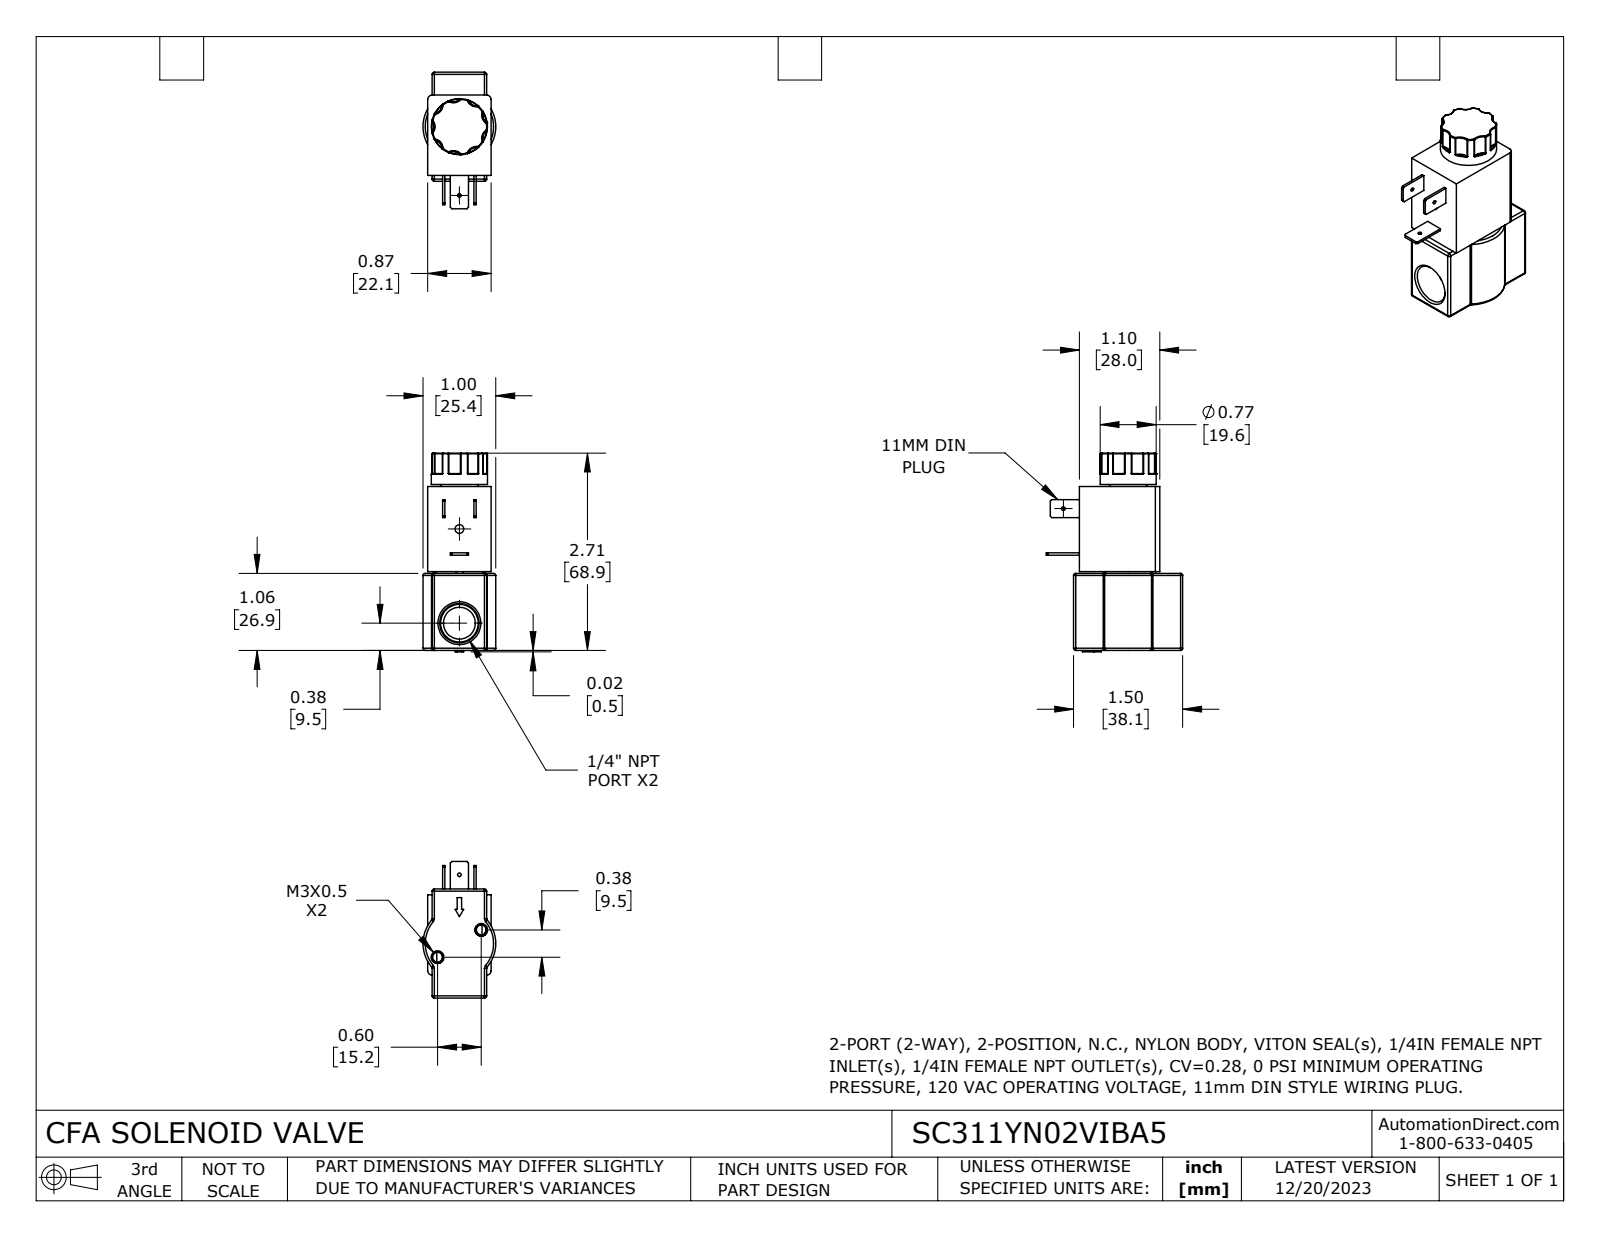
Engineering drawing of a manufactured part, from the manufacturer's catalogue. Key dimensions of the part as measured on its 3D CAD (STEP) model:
Part name (STEP PRODUCT): SC311YN02VIBA5
STEP written by: SolidWorks 2023 (CONFIG_CONTROL_DESIGN)
Units: inches
Bodies: 1 solid, 383 faces (62 planar, 117 cylindrical, 204 other)
Overall size (bounding box): 2.732 × 1.877 × 1
Volume: 2.397 in³ · Surface area: 17.71 in²
Round holes (diameter × count): ⌀0.05 ×2, ⌀0.136 ×2, ⌀0.12 ×1, ⌀0.438 ×1
Round bosses / shafts (diameter × count): ⌀0.77 ×1
Partial cylindrical surfaces — rounded edges, fillets, slot ends (radius × count): R0.01 ×18, R0.03 ×16, R0.133 ×7, R0.06 ×2, R0.132 ×2, R0.295 ×2, R0.311 ×1, R0.5 ×1
Main face-to-face distances: 0.06, 0.81, 0.87, 1.104, 2.252, 1.06, 1.192, 0.75, 1.085, 0.025
Hole centre spacings: 0.707, 0.815, 1.172, 1.293
